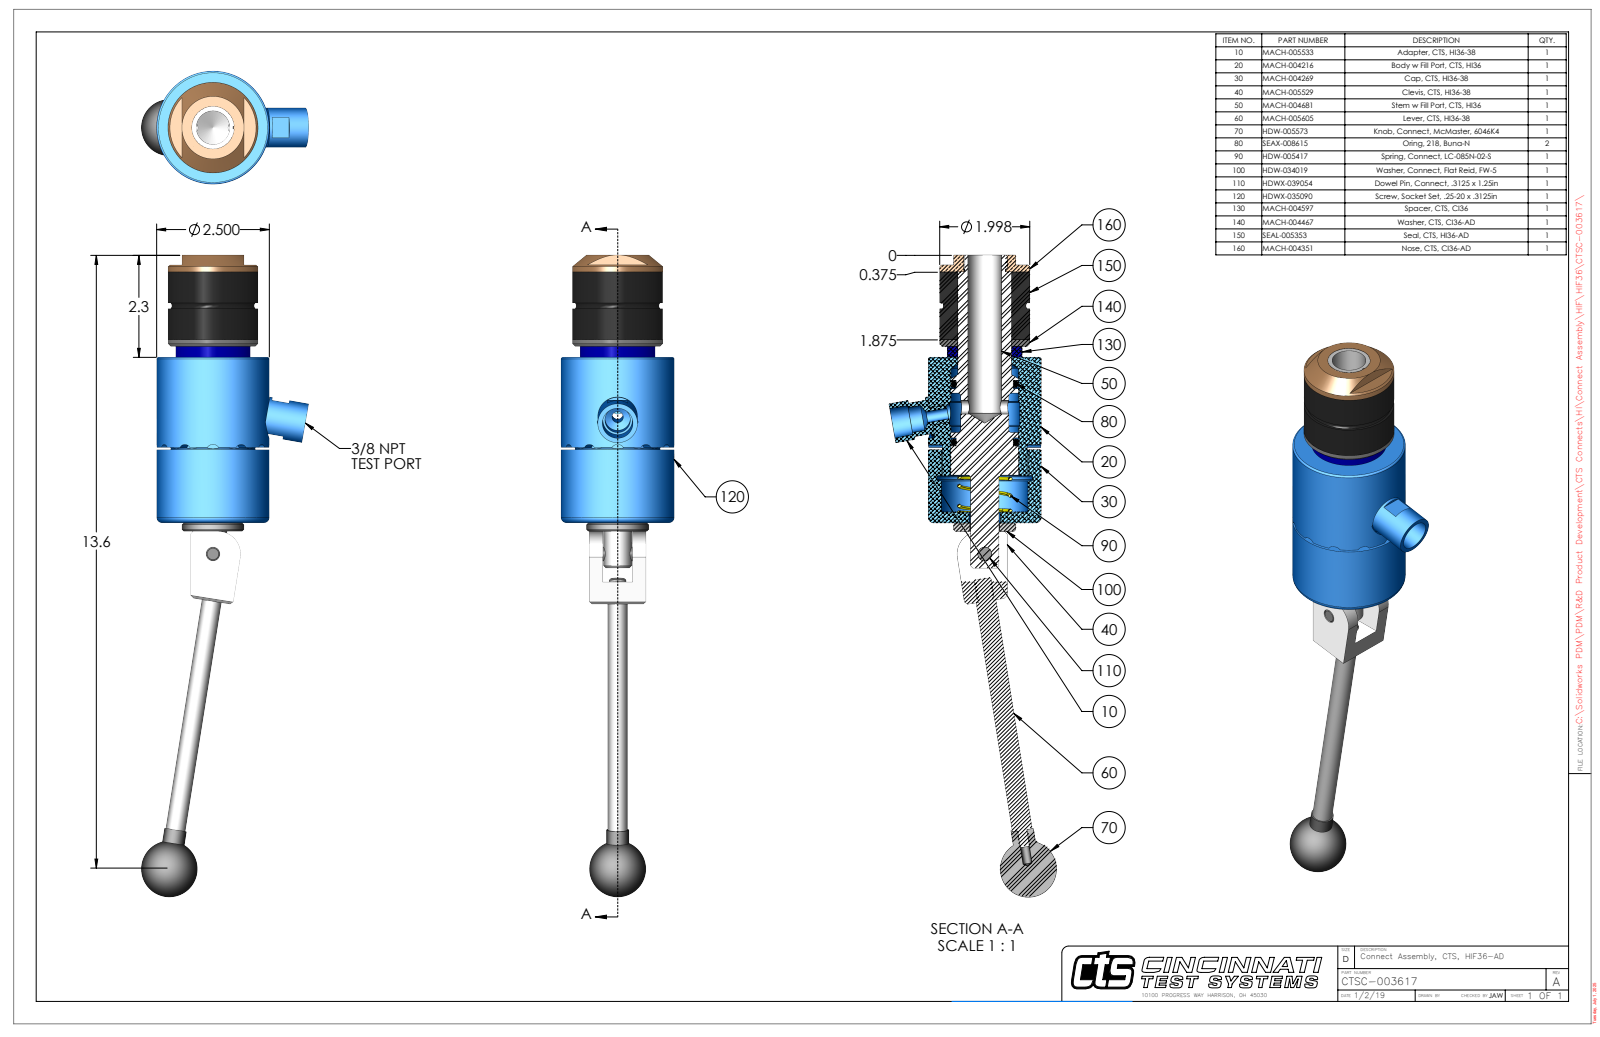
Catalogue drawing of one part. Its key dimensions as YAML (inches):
part_name: "CTSC-003617"
step_written_by: "SolidWorks 2023 (AUTOMOTIVE_DESIGN)"
units: inches
bodies: {solids: 10, faces: 318, planar: 117, cylindrical: 127, other: 74}
overall_size: [14.215, 3.716, 2.5]
volume: 26.61
surface_area: 133.6
round_holes:
  - {diameter: 0.201, count: 2}
  - {diameter: 0.15, count: 1}
  - {diameter: 0.25, count: 1}
  - {diameter: 0.311, count: 1}
  - {diameter: 0.312, count: 1}
  - {diameter: 0.313, count: 1}
  - {diameter: 0.314, count: 1}
  - {diameter: 0.562, count: 1}
  - {diameter: 0.656, count: 1}
  - {diameter: 0.696, count: 1}
  - {diameter: 0.75, count: 1}
  - {diameter: 0.922, count: 1}
round_bosses_or_shafts:
  - {diameter: 2.5, count: 1}
  - {diameter: 1.998, count: 1}
  - {diameter: 1.875, count: 1}
  - {diameter: 1.656, count: 1}
  - {diameter: 1.38, count: 1}
  - {diameter: 1.186, count: 1}
  - {diameter: 1, count: 1}
  - {diameter: 0.904, count: 1}
partial_cylinders:
  - {radius: 0.12, count: 12}
  - {radius: 0.029, count: 2}
  - {radius: 0.19, count: 1}
  - {radius: 0.195, count: 1}
  - {radius: 0.444, count: 1}
  - {radius: 0.47, count: 1}
  - {radius: 0.5, count: 1}
  - {radius: 1.172, count: 1}
face_to_face_distances: [5.555, 3.668, 1.887, 1.5, 4.055, 0.387, 3.905, 0.237, 0.15, 1.65]
hole_center_spacings: [0.74, 2.118, 2.858]
